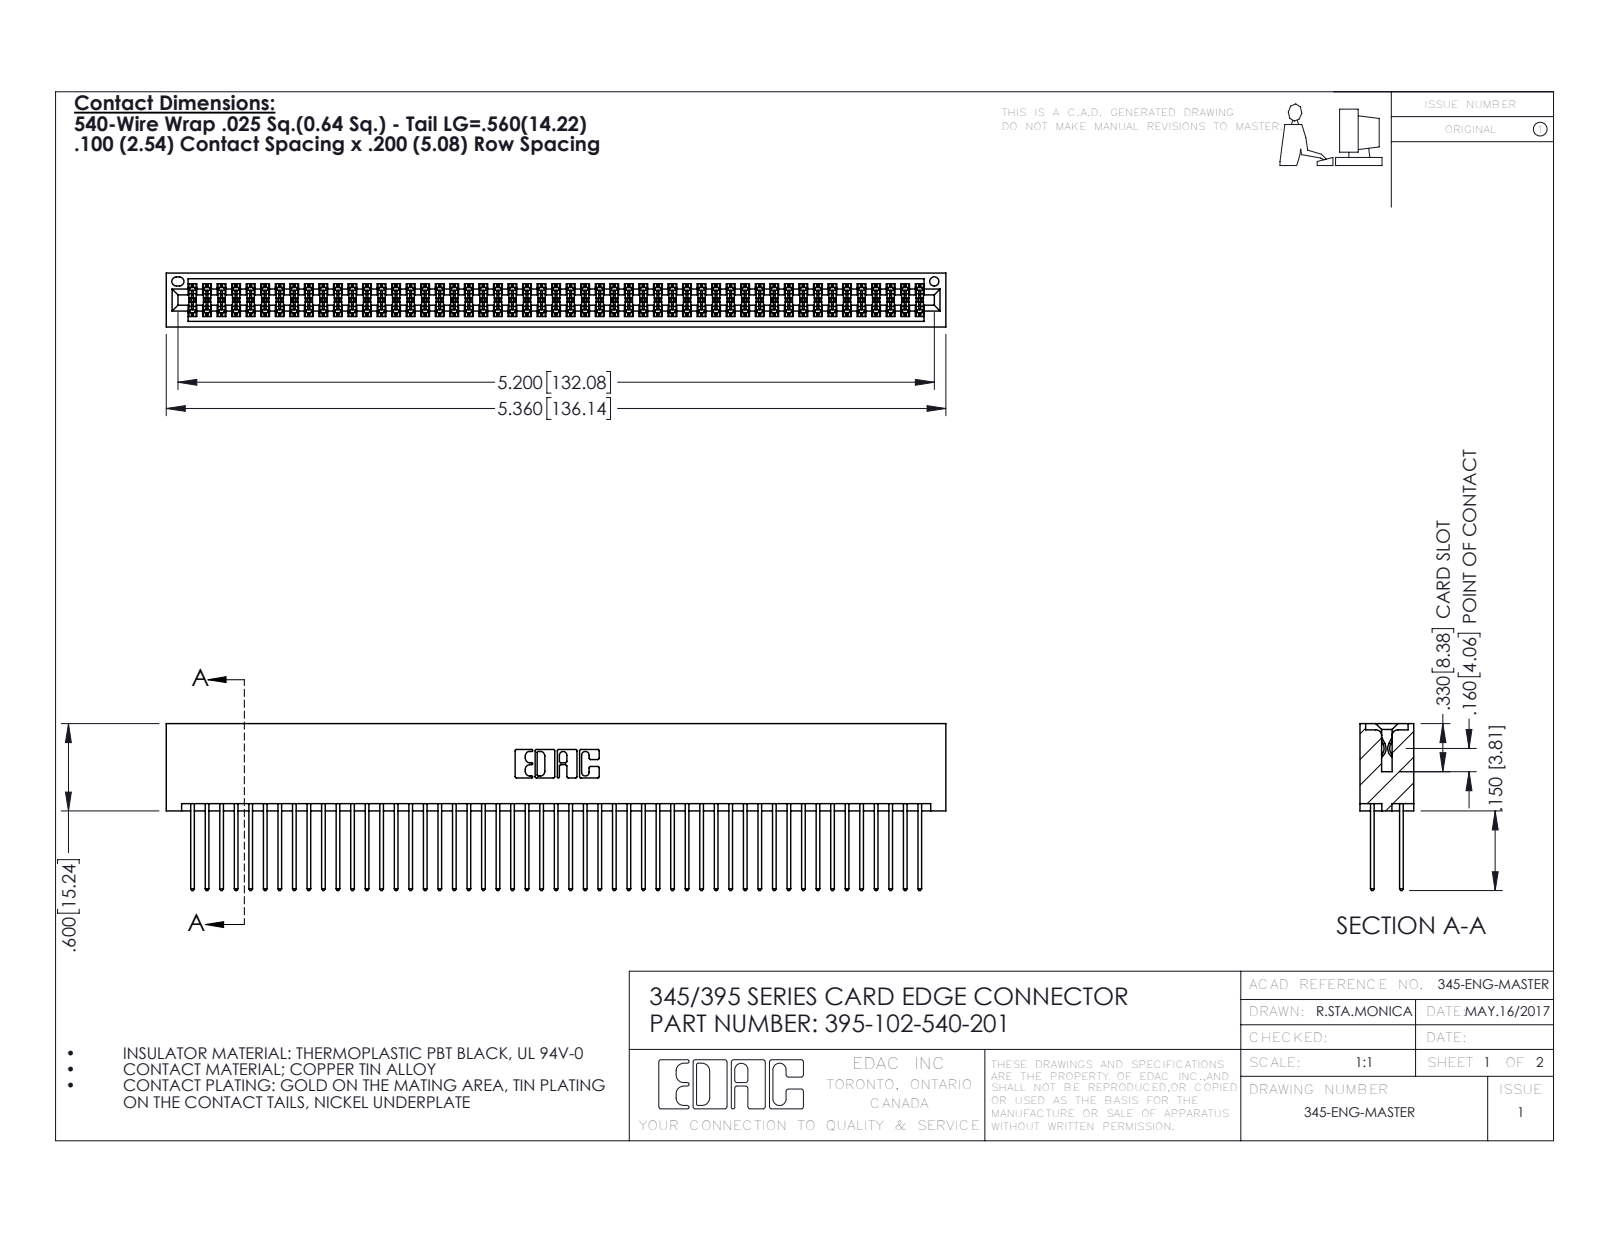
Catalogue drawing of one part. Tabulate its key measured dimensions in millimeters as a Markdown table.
| quantity | value |
| --- | --- |
| part name | 395-102-540-201; 345-292-001_345-293-140; 345 Part_No Mounting Lugs |
| STEP written by | SolidWorks 2016 (CONFIG_CONTROL_DESIGN) |
| units | millimeters |
| bodies | 103 solids, 5218 faces (3442 planar, 1776 cylindrical, 0 other) |
| overall size | 136.1 × 29.1 × 9.4 |
| volume | 14 300 mm³ |
| surface area | 23 430 mm² |
| round holes (diameter × count) | 1.6 × 1 |
| partial cylindrical surfaces (radius × count) | 0.2 × 153, 0.3 × 102, 0.3 × 22, 0.2 × 6, 0.8 × 6, 0.7 × 3, 0.4 × 2, 0.5 × 2 |
| main face-to-face distances | 7.6, 1.8, 5.1, 2.5, 6.9, 0.6, 5.7, 9.4, 4.4, 3.8 |
